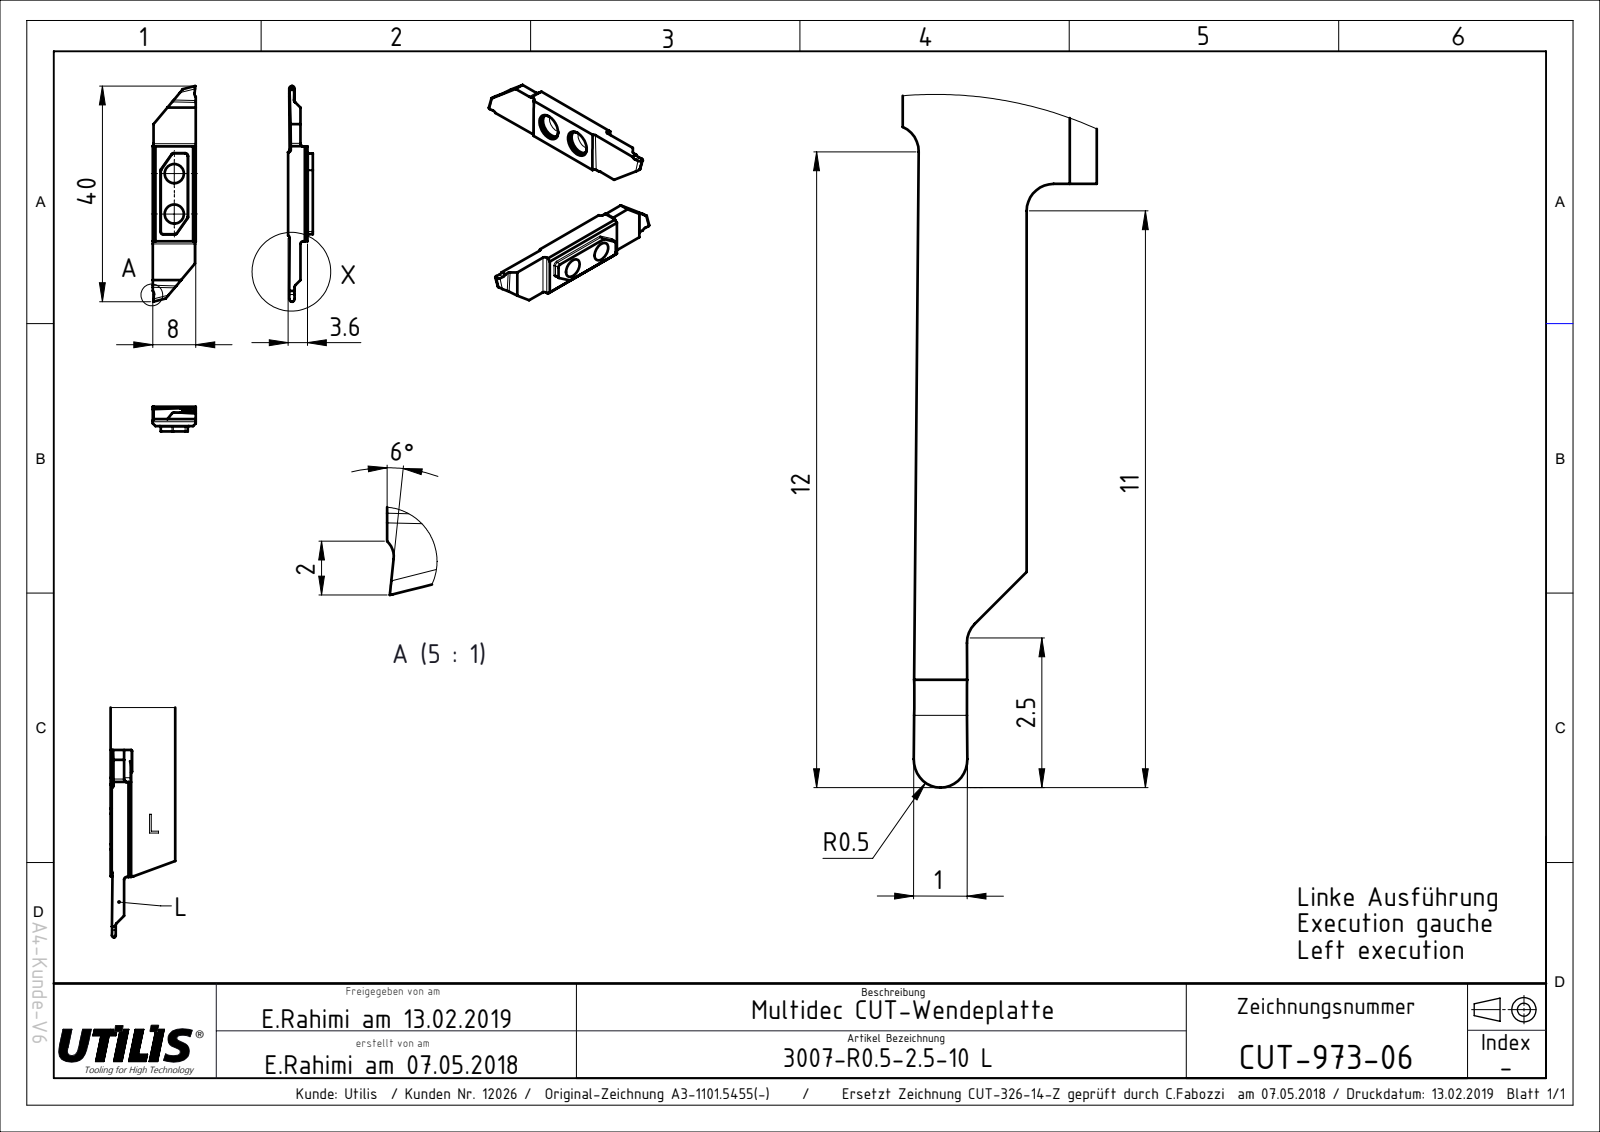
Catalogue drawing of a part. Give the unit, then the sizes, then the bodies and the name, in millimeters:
Units: millimetres
Overall size (bounding box): 40 × 8 × 3.6
Round holes (diameter × count): ⌀3.55 ×2
Partial cylindrical surfaces — rounded edges, fillets, slot ends (radius × count): R0.5 ×8, R0.8 ×2, R1 ×2
Main face-to-face distances: 3.6, 2.3, 1.3, 8, 7.85, 22.54, 0.65, 7.7, 17.6, 7.58
Hole centre spacings: 7.5
Volume: 675 mm³ · Surface area: 813 mm²
Bodies: 1 solid, 40 faces (22 planar, 18 cylindrical, 0 other)
Part name (STEP PRODUCT): CUT-973; ASME Y14.5
STEP written by: FormatWorks Professional (AP242_MANAGED_MODEL_BASED_3D_ENGINEERING_MIM_LF)
